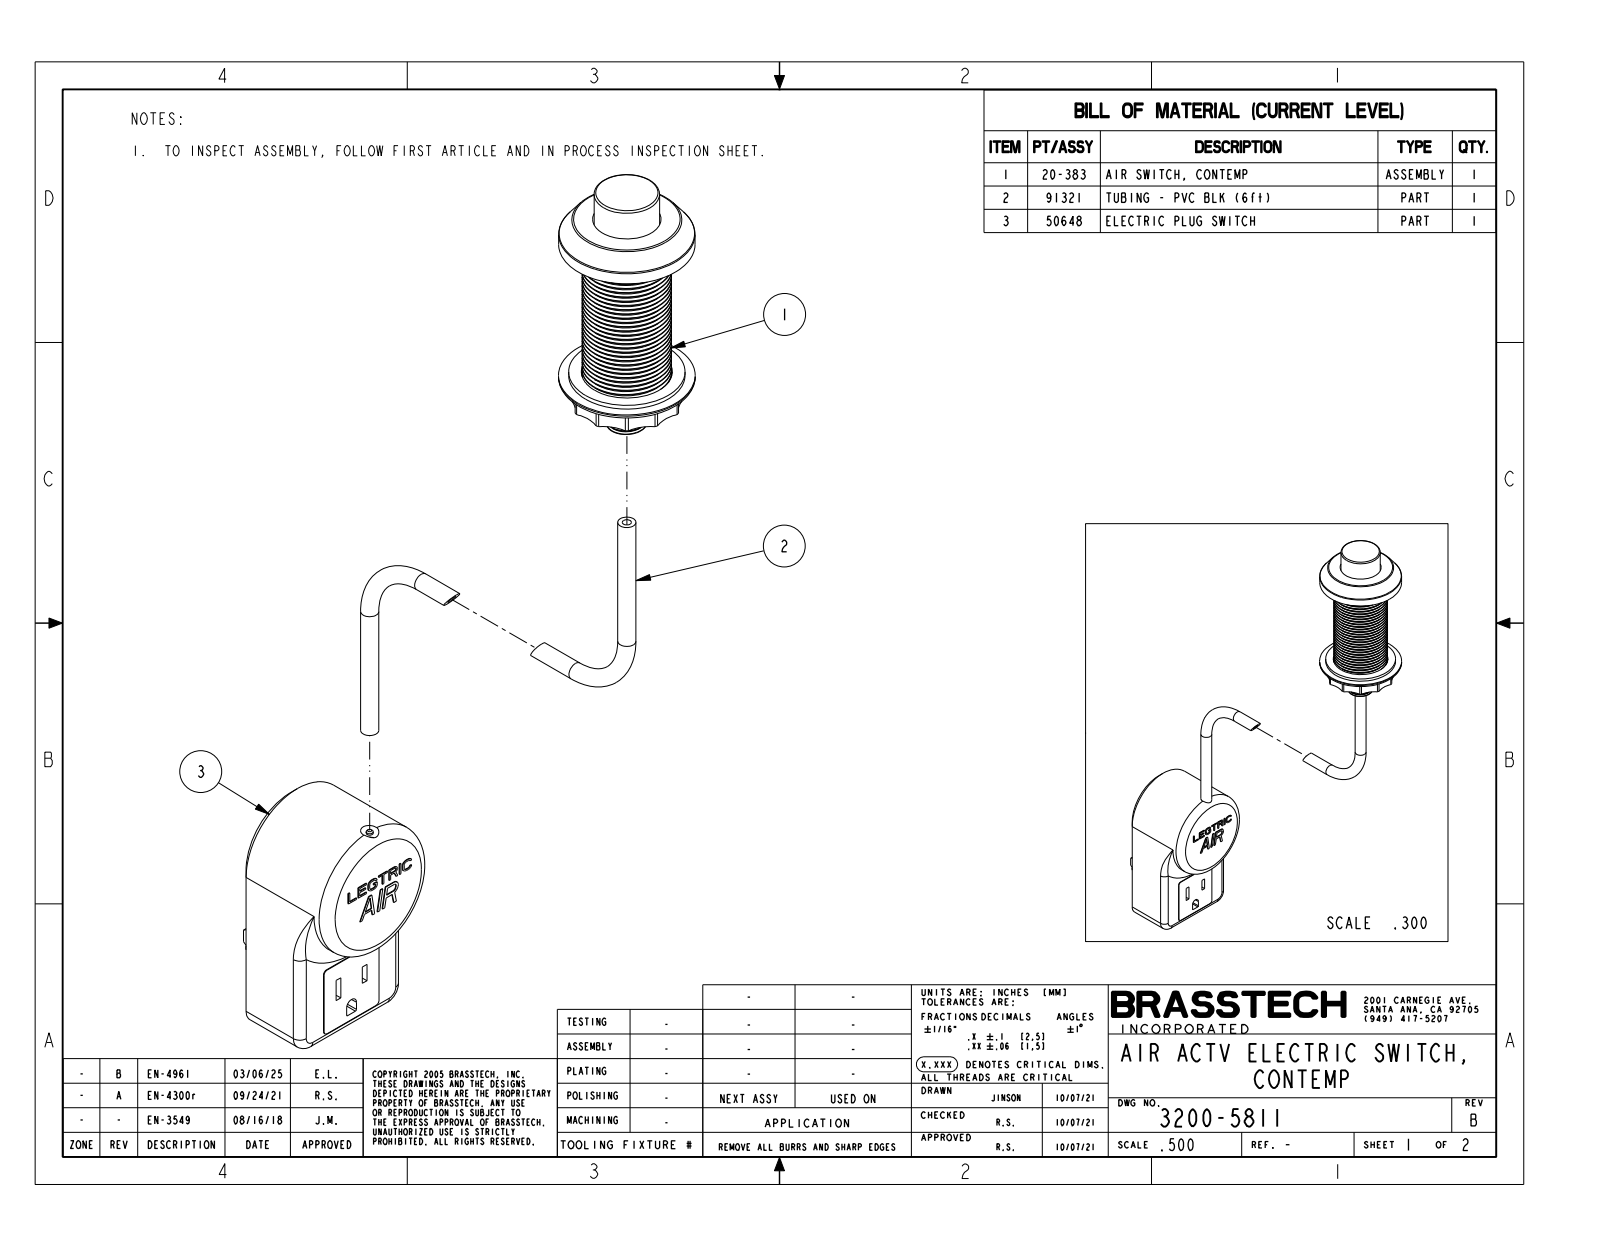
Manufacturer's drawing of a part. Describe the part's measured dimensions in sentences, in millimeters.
The part is named "3200-5811". Its 3-D file was written by "CREO PARAMETRIC BY PTC INC, 2018400 (AUTOMOTIVE_DESIGN)". It is 3 solids with 470 faces: 253 planar, 149 cylindrical and 68 other. Overall it measures 329.8 by 211.2 by 50.5 millimeters. Its volume is 232 700 cubic millimeters and its surface area 43 760 square millimeters. Round holes: 4 of diameter 3.2, 1 of diameter 23.9, 1 of diameter 31.8. Round bosses or shafts: 3 of diameter 6.4, 1 of diameter 50.5, 1 of diameter 47.8, 1 of diameter 47.6, 1 of diameter 40.6, 1 of diameter 31.2, 1 of diameter 29.3, 1 of diameter 28.8. Partial cylindrical surfaces (rounded edges, fillets, slot ends): 12 of radius 12.7, 4 of radius 1.5, 3 of radius 3.2, 2 of radius 0.5, 2 of radius 6.4, 1 of radius 2.4, 1 of radius 20.6. The main face-to-face distances are 50.5, 43.2, 2, 9.1, 306.3, 13.2, 30, 317.1, 10.8, 11.2. The hole center spacings are 127.
